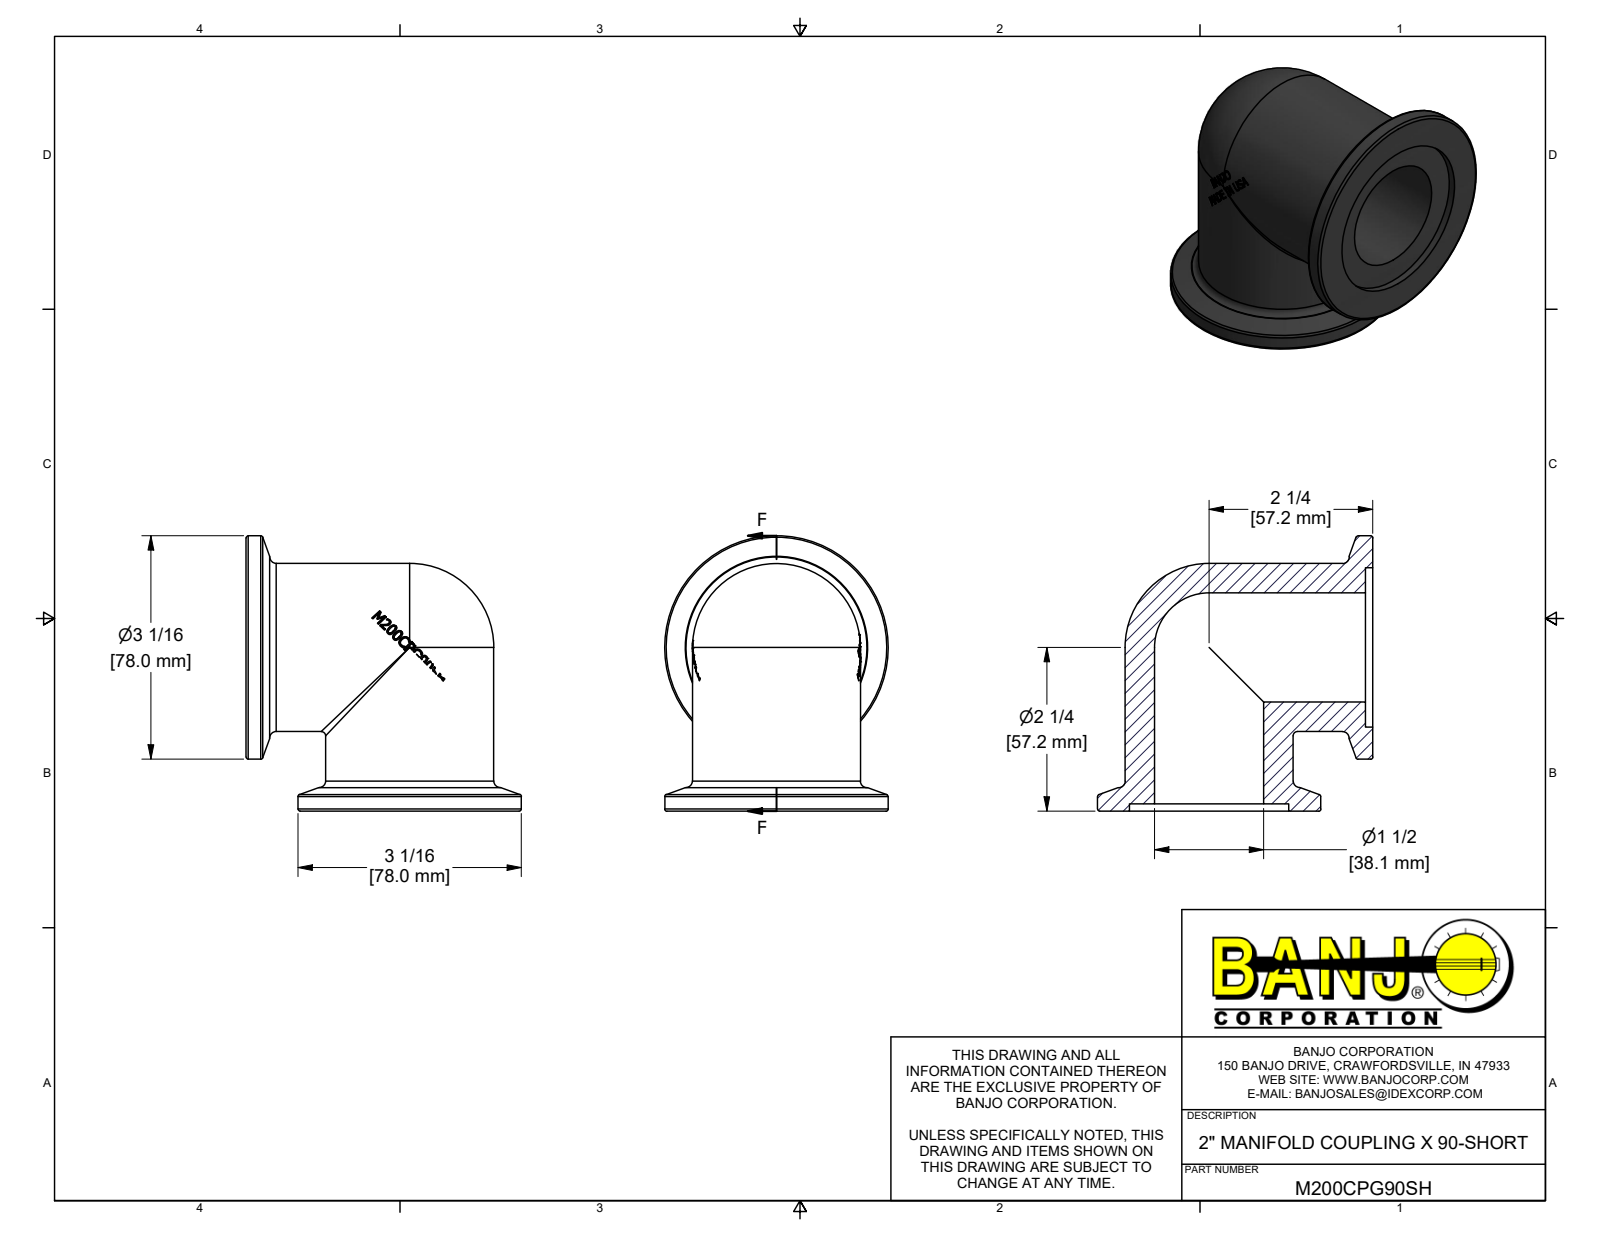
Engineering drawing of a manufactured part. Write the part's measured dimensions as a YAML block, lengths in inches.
part_name: "M200CPG90SH; M200CPG90SHU"
step_written_by: "Autodesk Inventor 2019 (AUTOMOTIVE_DESIGN)"
units: inches
bodies: {solids: 1, faces: 437, planar: 129, cylindrical: 53, other: 255}
overall_size: [3.785, 3.785, 3.07]
volume: 12.03
surface_area: 69.66
round_holes:
  - {diameter: 1.5, count: 2}
  - {diameter: 2.19, count: 2}
  - {diameter: 2.31, count: 1}
round_bosses_or_shafts:
  - {diameter: 3.07, count: 2}
  - {diameter: 2.31, count: 1}
partial_cylinders:
  - {radius: 1.135, count: 2}
face_to_face_distances: [0.1, 0.324, 0.224, 0.015, 0.016, 0.12, 0.282, 0.198, 0.09, 0.019]
